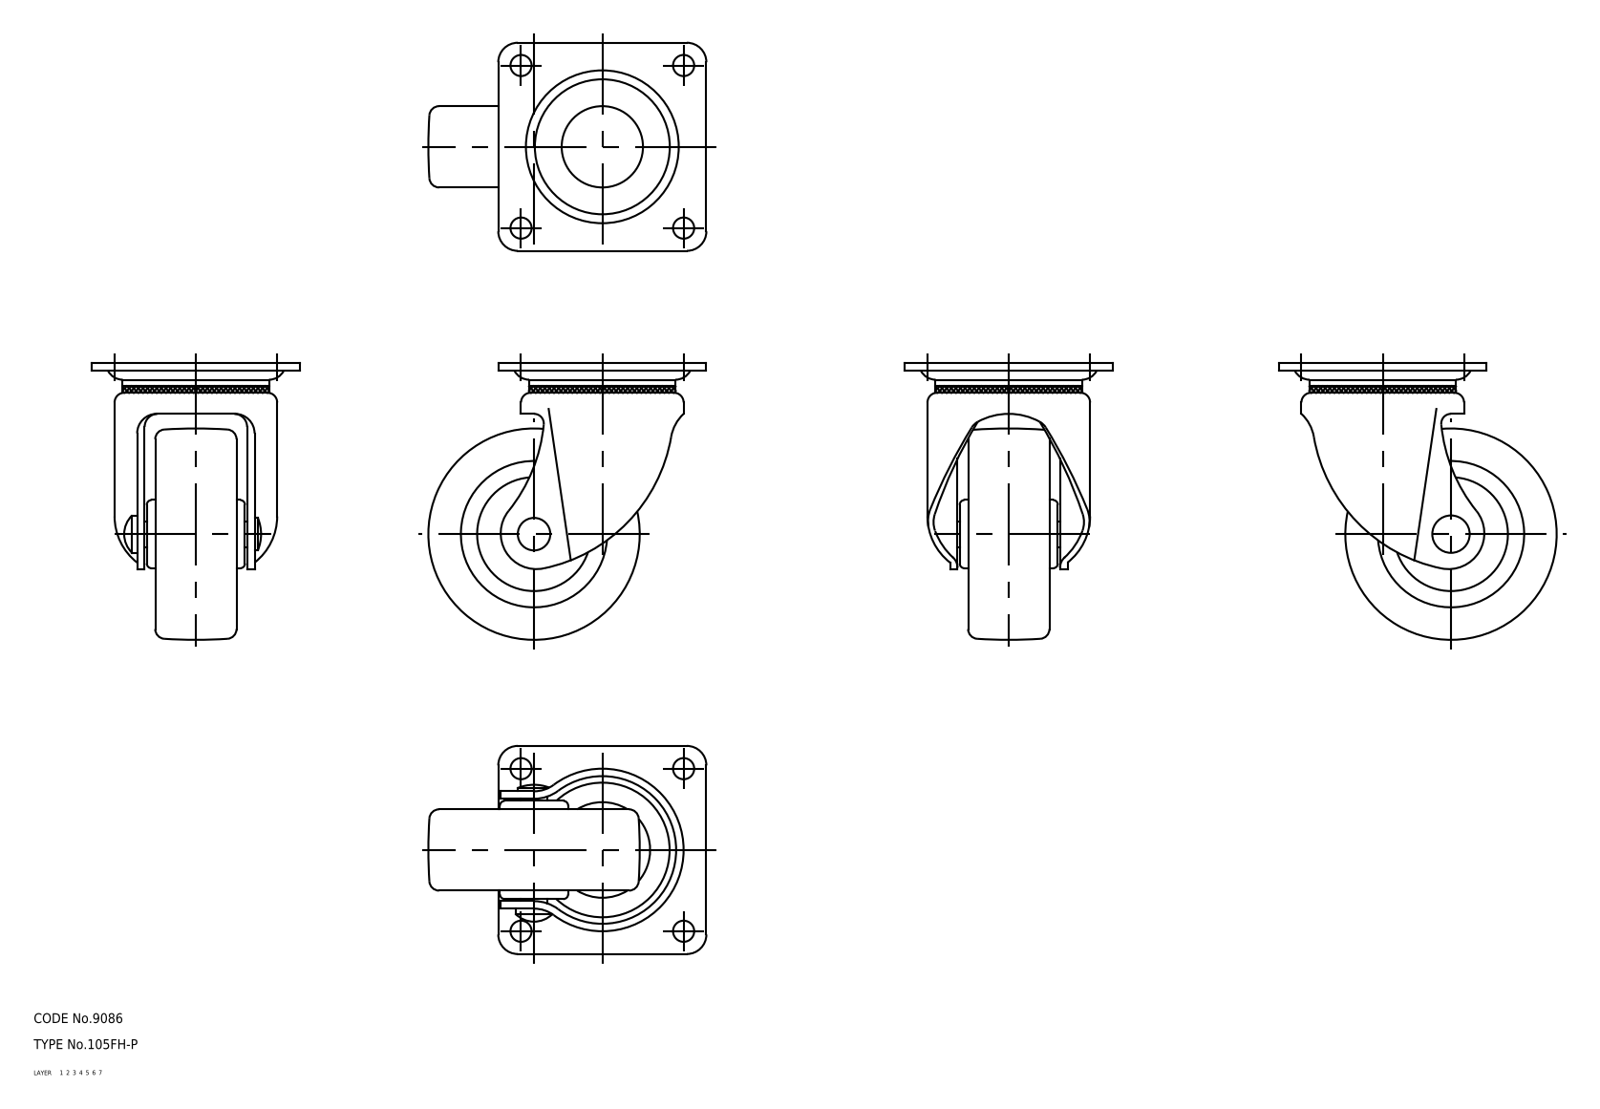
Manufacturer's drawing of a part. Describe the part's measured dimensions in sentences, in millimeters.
The part is named "wheel; mounting plate; main shaft; axle (+1 more)". Its 3-D file was written by "CADfix (AUTOMOTIVE_DESIGN)". It is 5 solids with 183 faces: 0 planar, 0 cylindrical and 183 other. Overall it measures 85.5 by 85 by 64 millimeters. Its volume is 112 275 cubic millimeters and its surface area 39 322 square millimeters.
